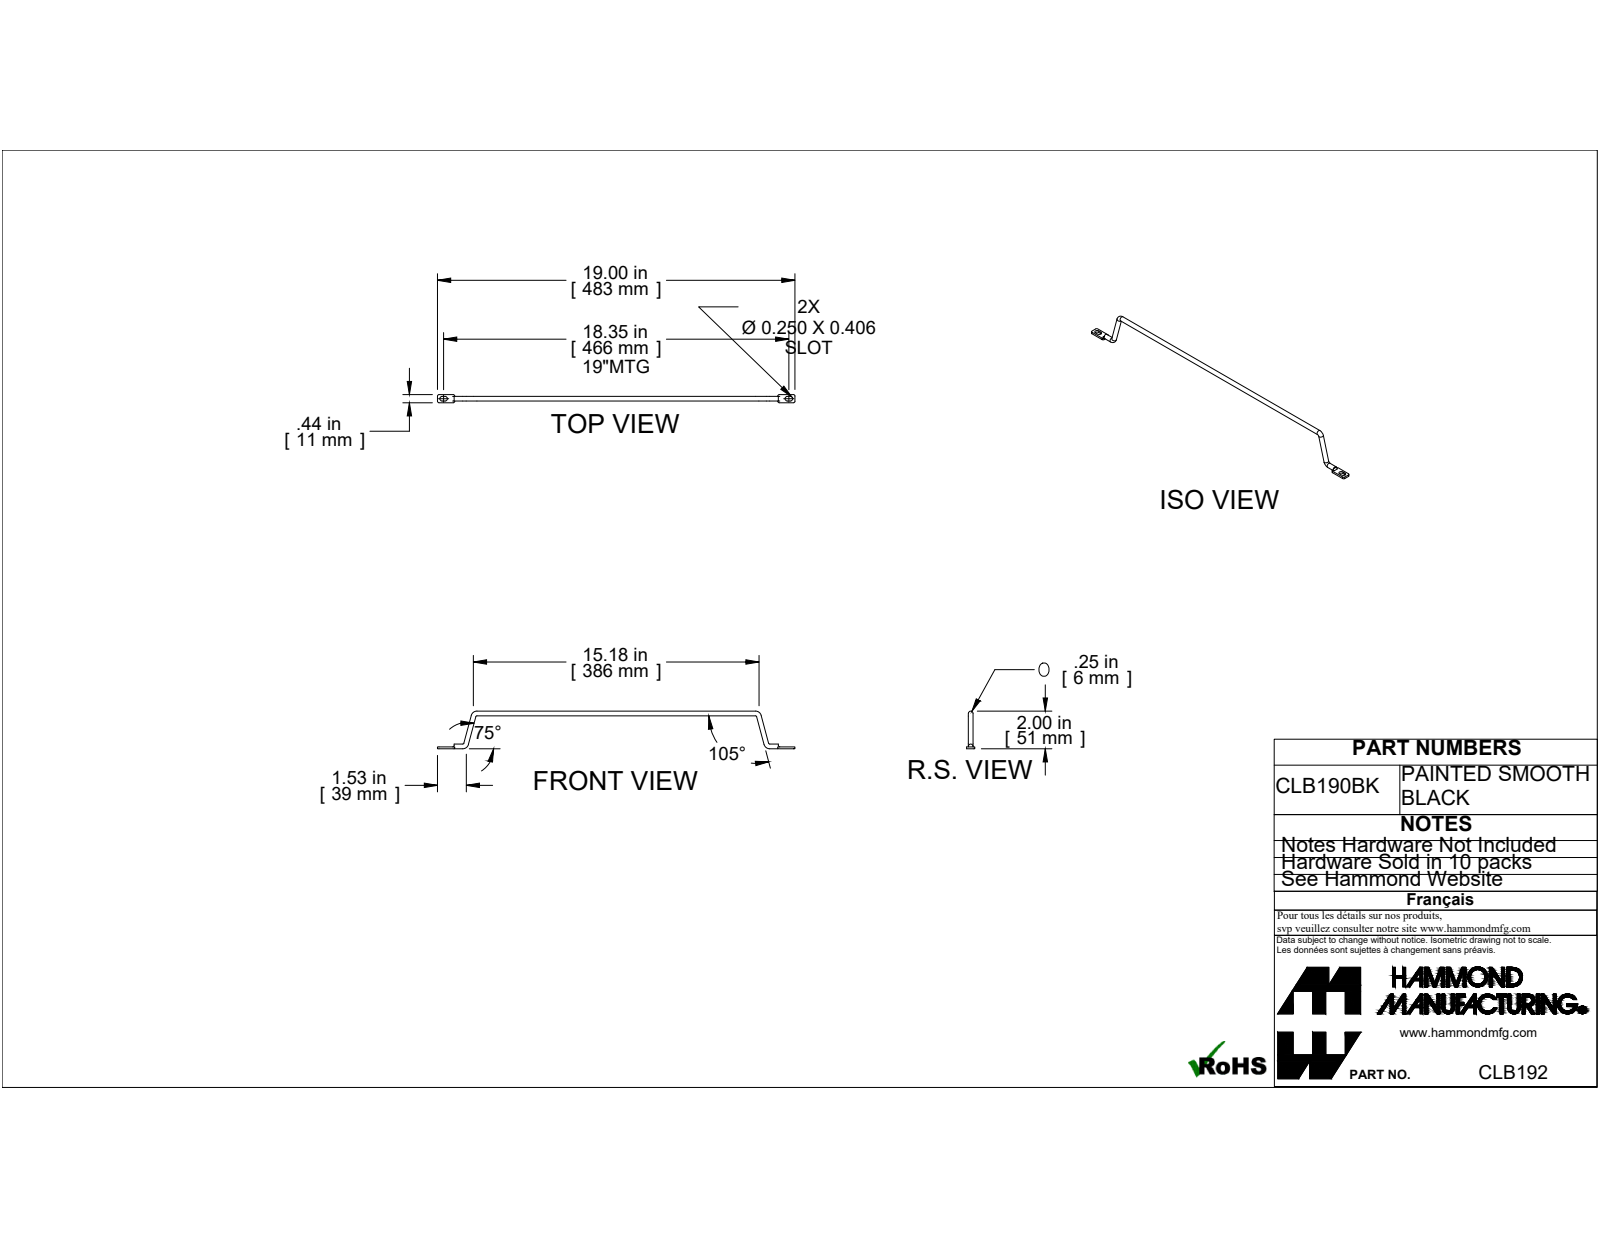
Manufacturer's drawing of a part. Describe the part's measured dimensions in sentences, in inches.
Its 3-D file was written by "Unknown (AUTOMOTIVE_DESIGN)". It is 1 solid with 43 faces: 20 planar, 19 cylindrical and 4 other. Overall it measures 19 by 2 by 0.435 inches. Its volume is 1.025 cubic inches and its surface area 17.38 square inches. Round bosses or shafts: 4 of diameter 0.25. Partial cylindrical surfaces (rounded edges, fillets, slot ends): 10 of radius 0.08, 4 of radius 0.125. The main face-to-face distances are 0.1, 0.435, 0.093, 0.342, 0.25, 19, 0.885, 18.115, 0.917, 18.083.
